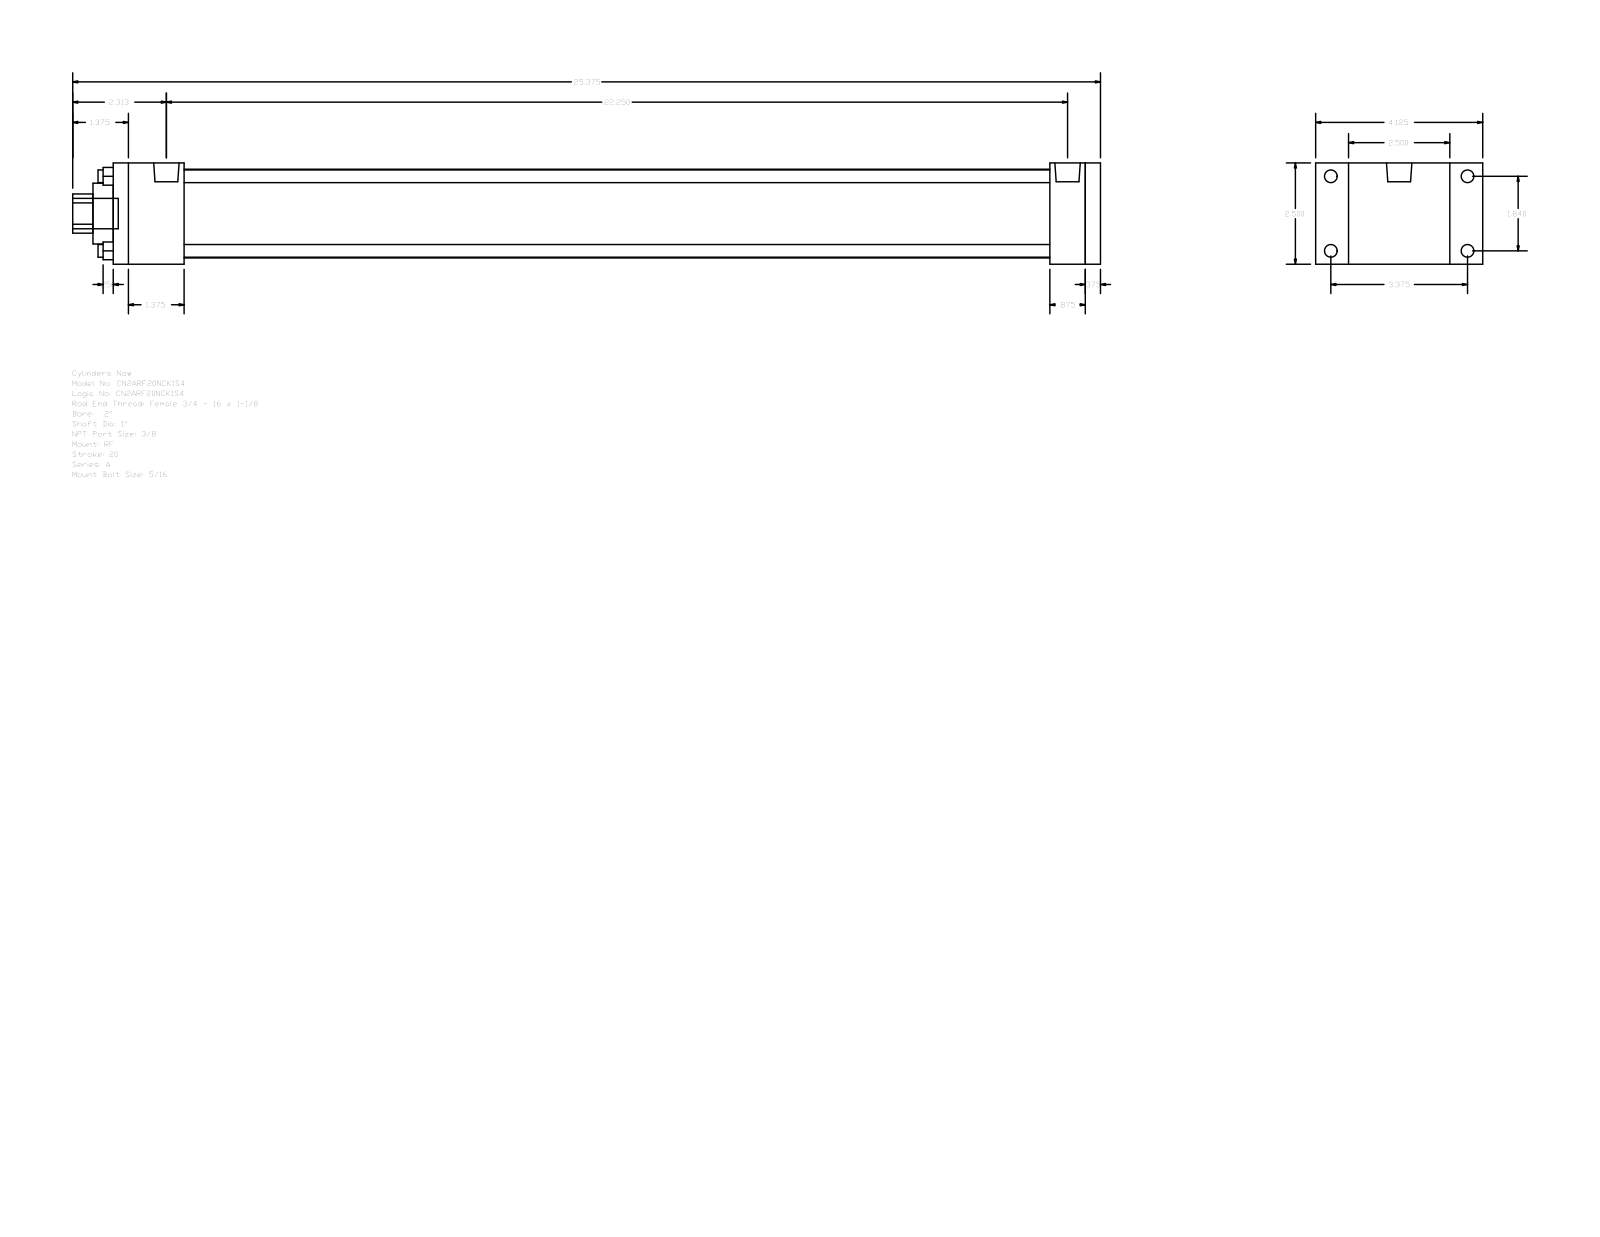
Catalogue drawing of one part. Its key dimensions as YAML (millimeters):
part_name: "A_RF__0200_1"
step_written_by: "GSSL Pune (CONFIG_CONTROL_DESIGN)"
units: millimeters
bodies: {solids: 0, faces: 92, planar: 64, cylindrical: 28, other: 0}
overall_size: [644.52, 104.78, 63.5]
round_holes:
  - {diameter: 7.94, count: 4}
  - {diameter: 25.4, count: 1}
  - {diameter: 38.1, count: 1}
  - {diameter: 55.63, count: 1}
round_bosses_or_shafts:
  - {diameter: 7.94, count: 4}
  - {diameter: 5.56, count: 4}
  - {diameter: 15.93, count: 2}
  - {diameter: 19.05, count: 1}
partial_cylinders:
  - {radius: 12.29, count: 1}
face_to_face_distances: [63.5, 9.52, 619.12, 609.6, 20.64, 44.45, 565.15, 574.67, 587.37, 542.92]
hole_center_spacings: [33.05, 46.74, 66.1]
